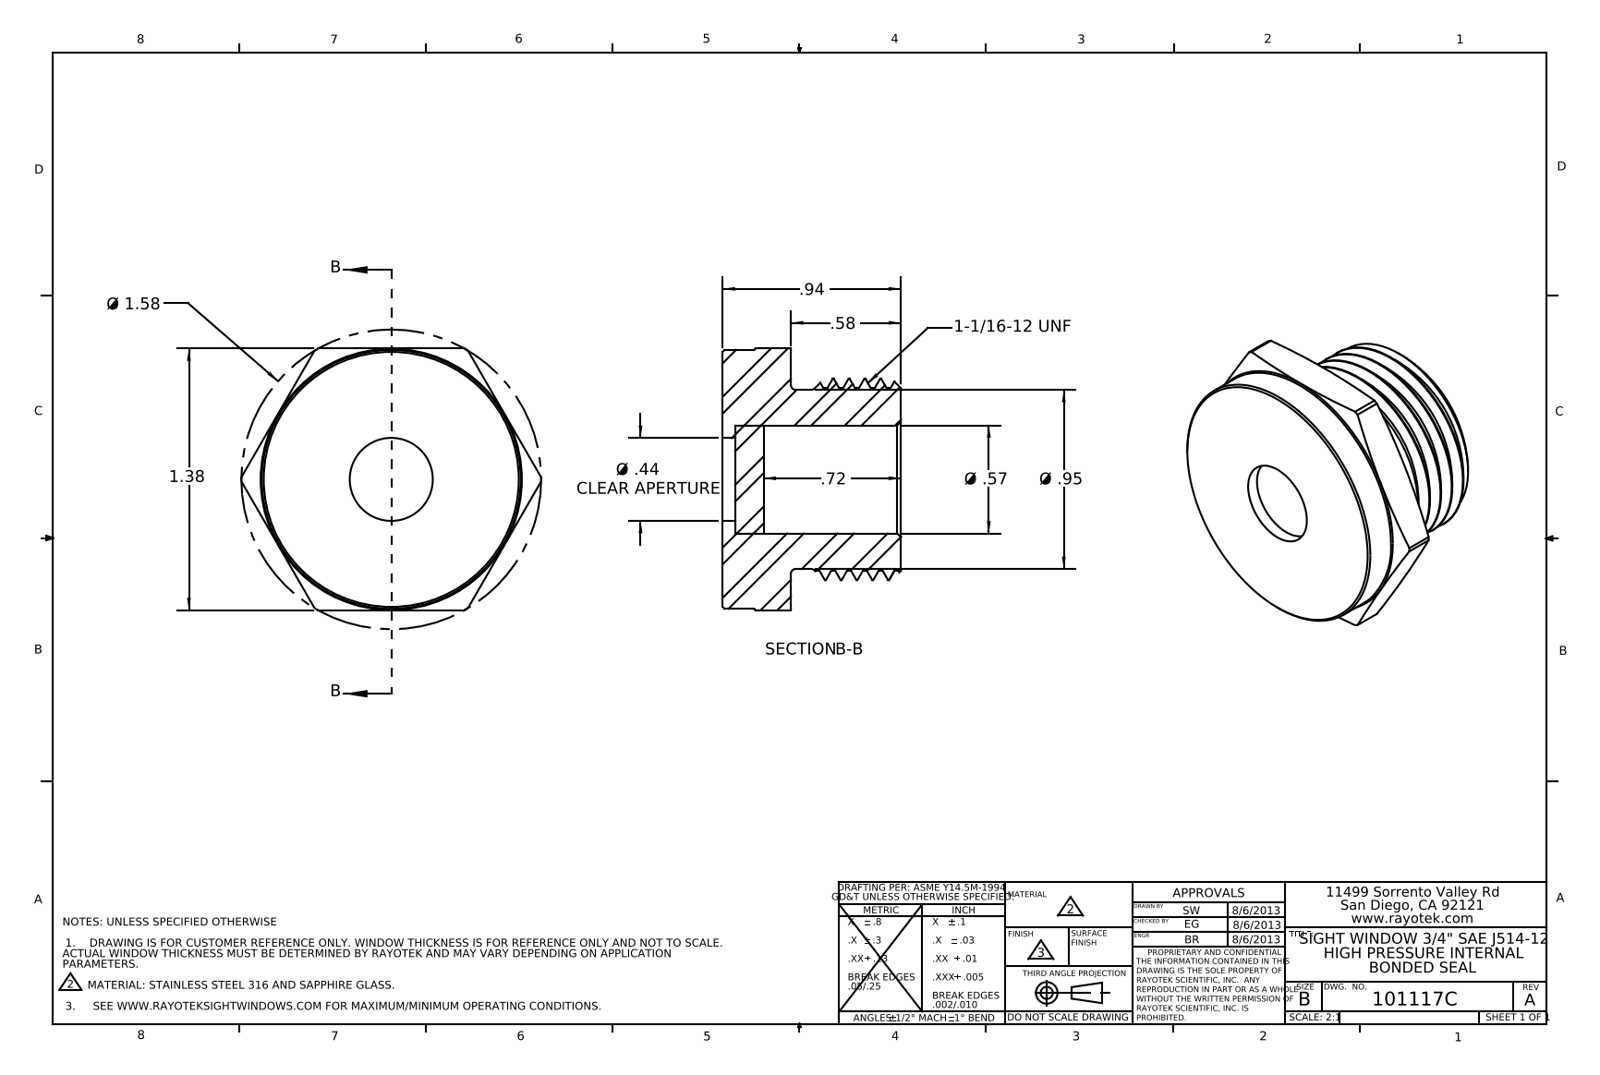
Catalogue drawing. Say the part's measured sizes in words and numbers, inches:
The part is named "403117". Its 3-D file was written by "SolidWorks 2012 (AUTOMOTIVE_DESIGN)". It is 2 solids with 61 faces: 12 planar, 26 cylindrical and 23 other. Overall it measures 1.581 by 1.38 by 0.94 inches. Its volume is 0.81 cubic inches and its surface area 9.669 square inches. Round holes: 1 of diameter 0.438, 1 of diameter 0.57. Round bosses or shafts: 1 of diameter 1.365, 1 of diameter 1.063, 1 of diameter 0.945. Partial cylindrical surfaces (rounded edges, fillets, slot ends): 1 of radius 0.791. The main face-to-face distances are 0.36, 0.58, 0.94, 1.38, 0.874, 0.294, 0.066, 0.724, 0.144, 0.15.
